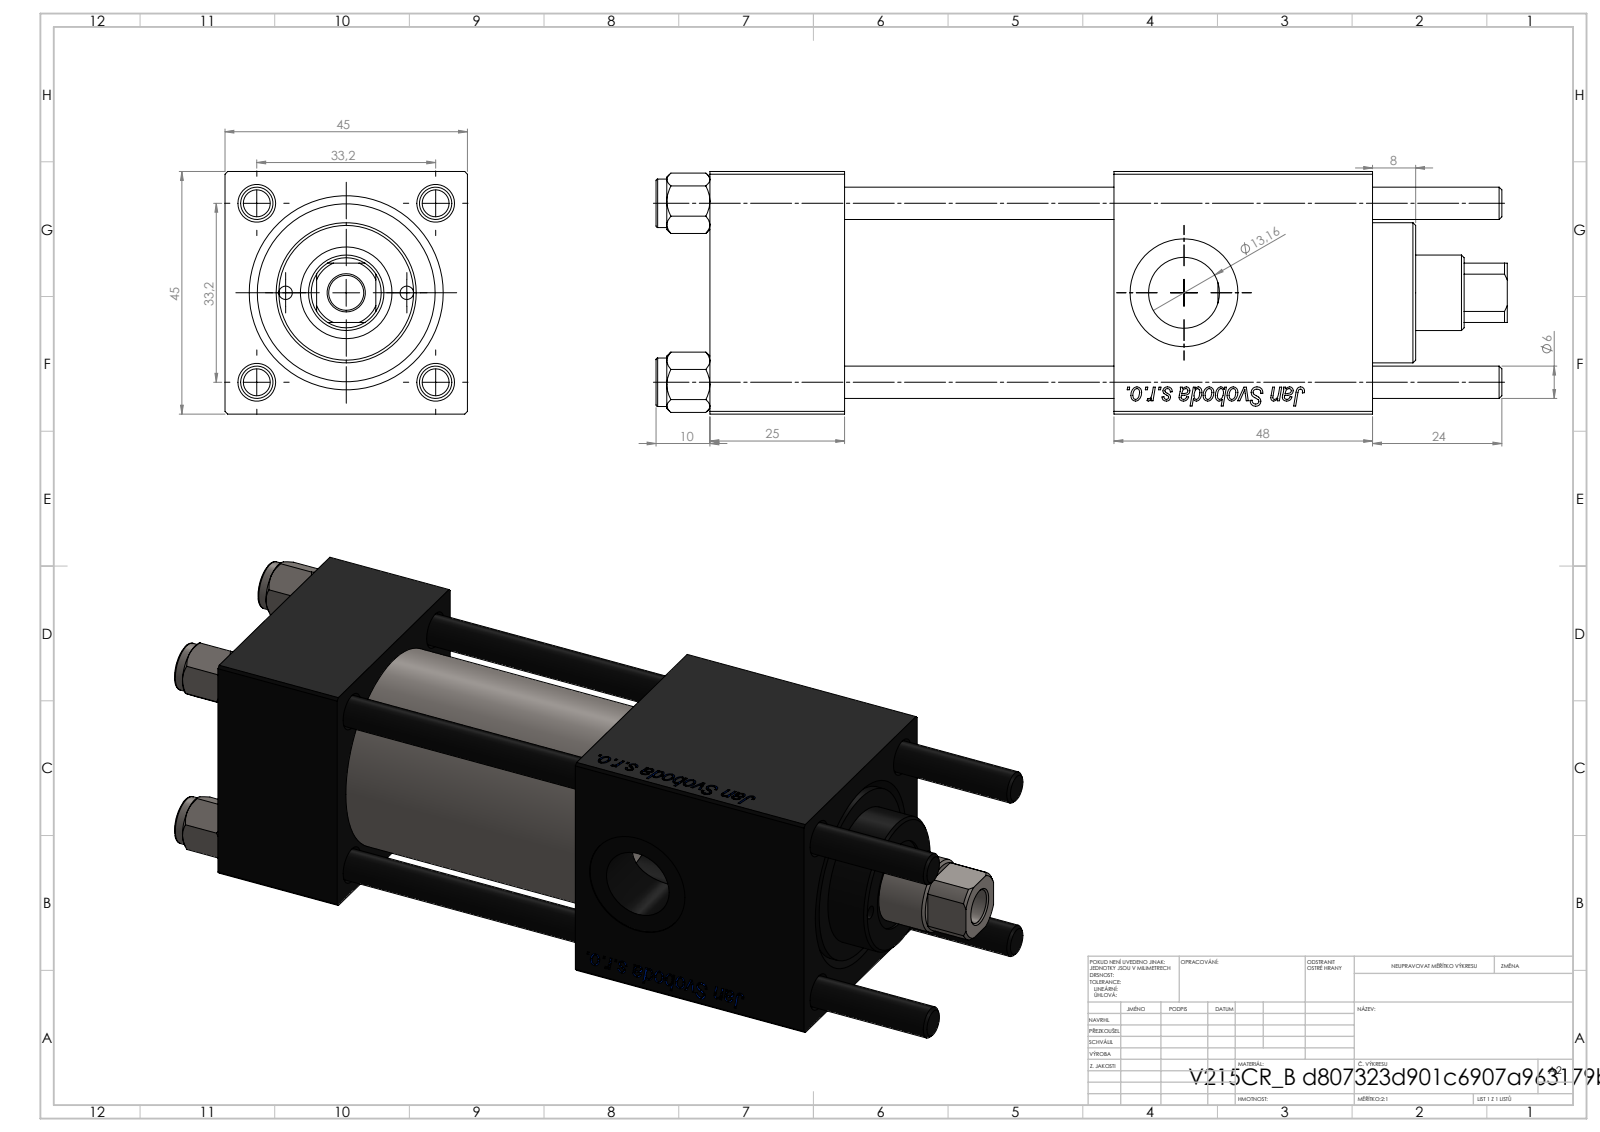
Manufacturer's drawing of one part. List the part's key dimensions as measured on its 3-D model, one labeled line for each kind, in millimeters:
Part name (STEP PRODUCT): V215CR_VCP_B; NUT_M5_B; V215_VC_A; V215CR_B_TYCINKA (+1 more)
STEP written by: SolidWorks 2019 (CONFIG_CONTROL_DESIGN)
Units: millimetres
Bodies: 11 solids, 1162 faces (431 planar, 83 cylindrical, 648 other)
Overall size (bounding box): 158 × 45 × 45
Volume: 198 169 mm³ · Surface area: 72 766 mm²
Round holes (diameter × count): ⌀6 ×4, ⌀2.5 ×2, ⌀7 ×2, ⌀13.16 ×2, ⌀20 ×2, ⌀6.5 ×1, ⌀14 ×1, ⌀17 ×1, ⌀24 ×1, ⌀32 ×1, ⌀33 ×1
Round bosses / shafts (diameter × count): ⌀9 ×4, ⌀38 ×1, ⌀26 ×1
Partial cylindrical surfaces — rounded edges, fillets, slot ends (radius × count): R6.5 ×1
Main face-to-face distances: 45, 25, 123, 98, 50, 75, 48, 94.3, 69.3, 19.3
Hole centre spacings: 17.44, 23.48, 32.42, 33.2, 11.25, 46.95, 22.5
